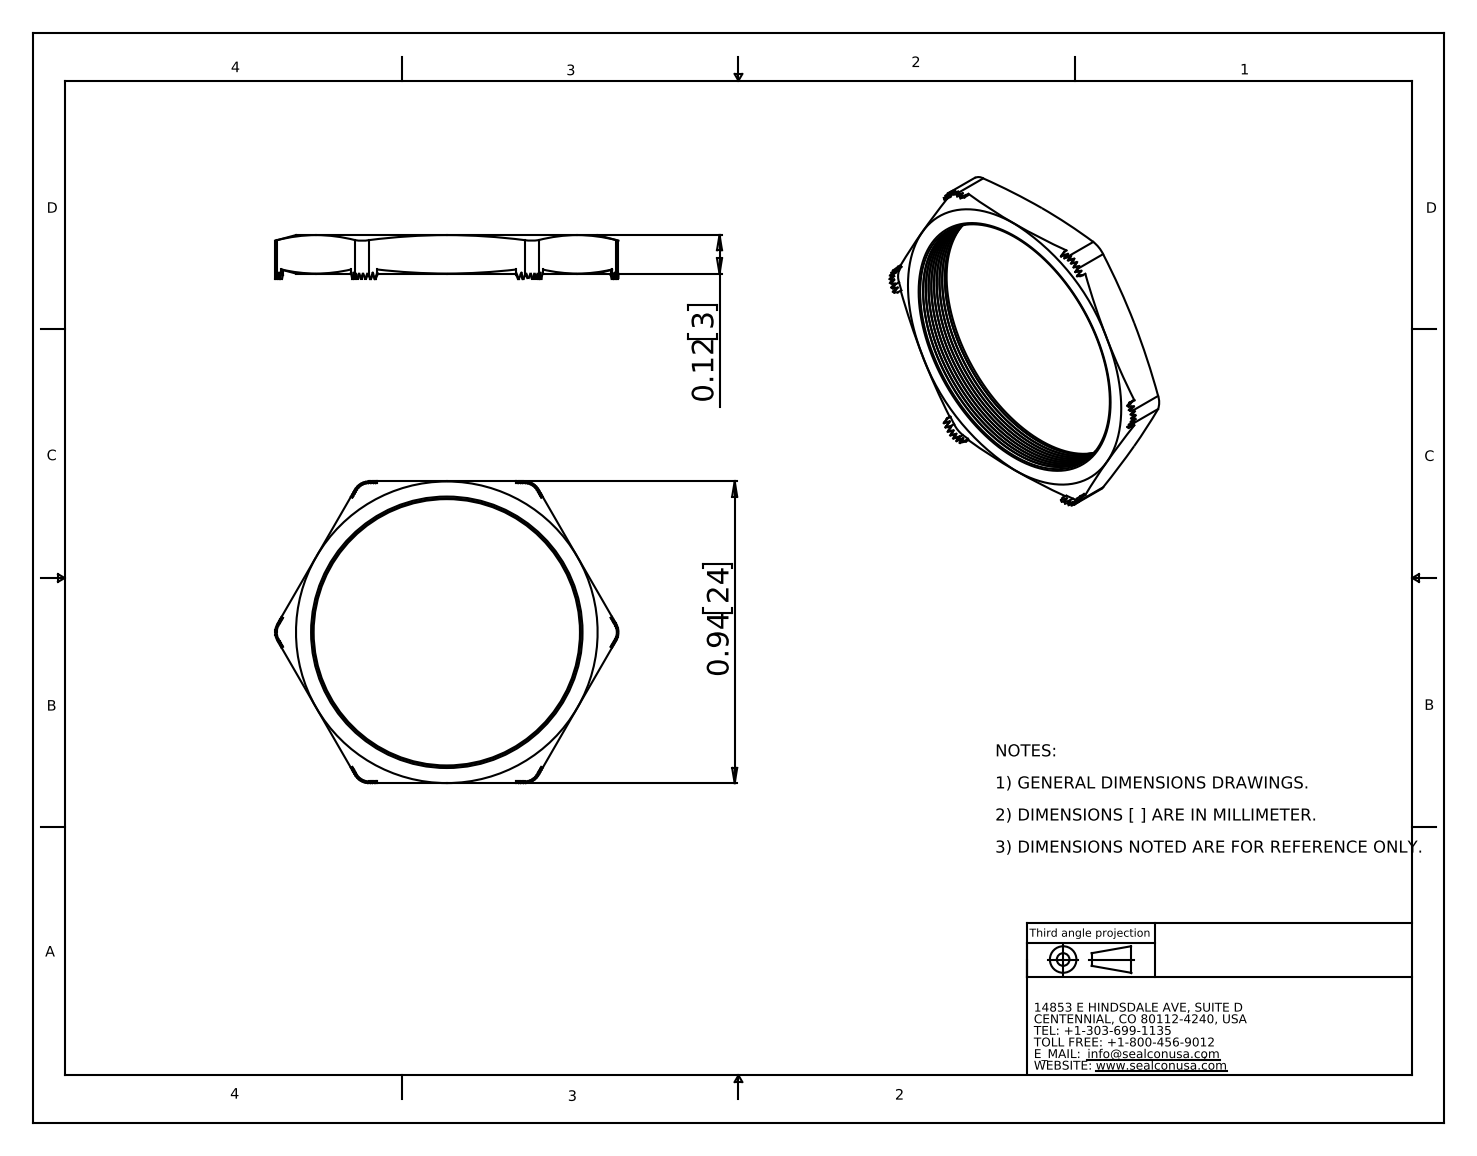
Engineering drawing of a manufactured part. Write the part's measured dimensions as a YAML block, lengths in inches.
part_name: "NN-13-BE"
step_written_by: "SolidWorks 2007 (CONFIG_CONTROL_DESIGN)"
units: inches
bodies: {solids: 1, faces: 206, planar: 116, cylindrical: 32, other: 58}
overall_size: [1.07, 0.94, 0.137]
volume: 0.025
surface_area: 1.421
round_holes:
  - {diameter: 0.83, count: 1}
partial_cylinders:
  - {radius: 0.045, count: 6}
  - {radius: 0.05, count: 6}
face_to_face_distances: [0.94, 0.12, 0.935, 0.93, 0.013, 0.026, 0.025, 0.051, 0.013, 0.039]
